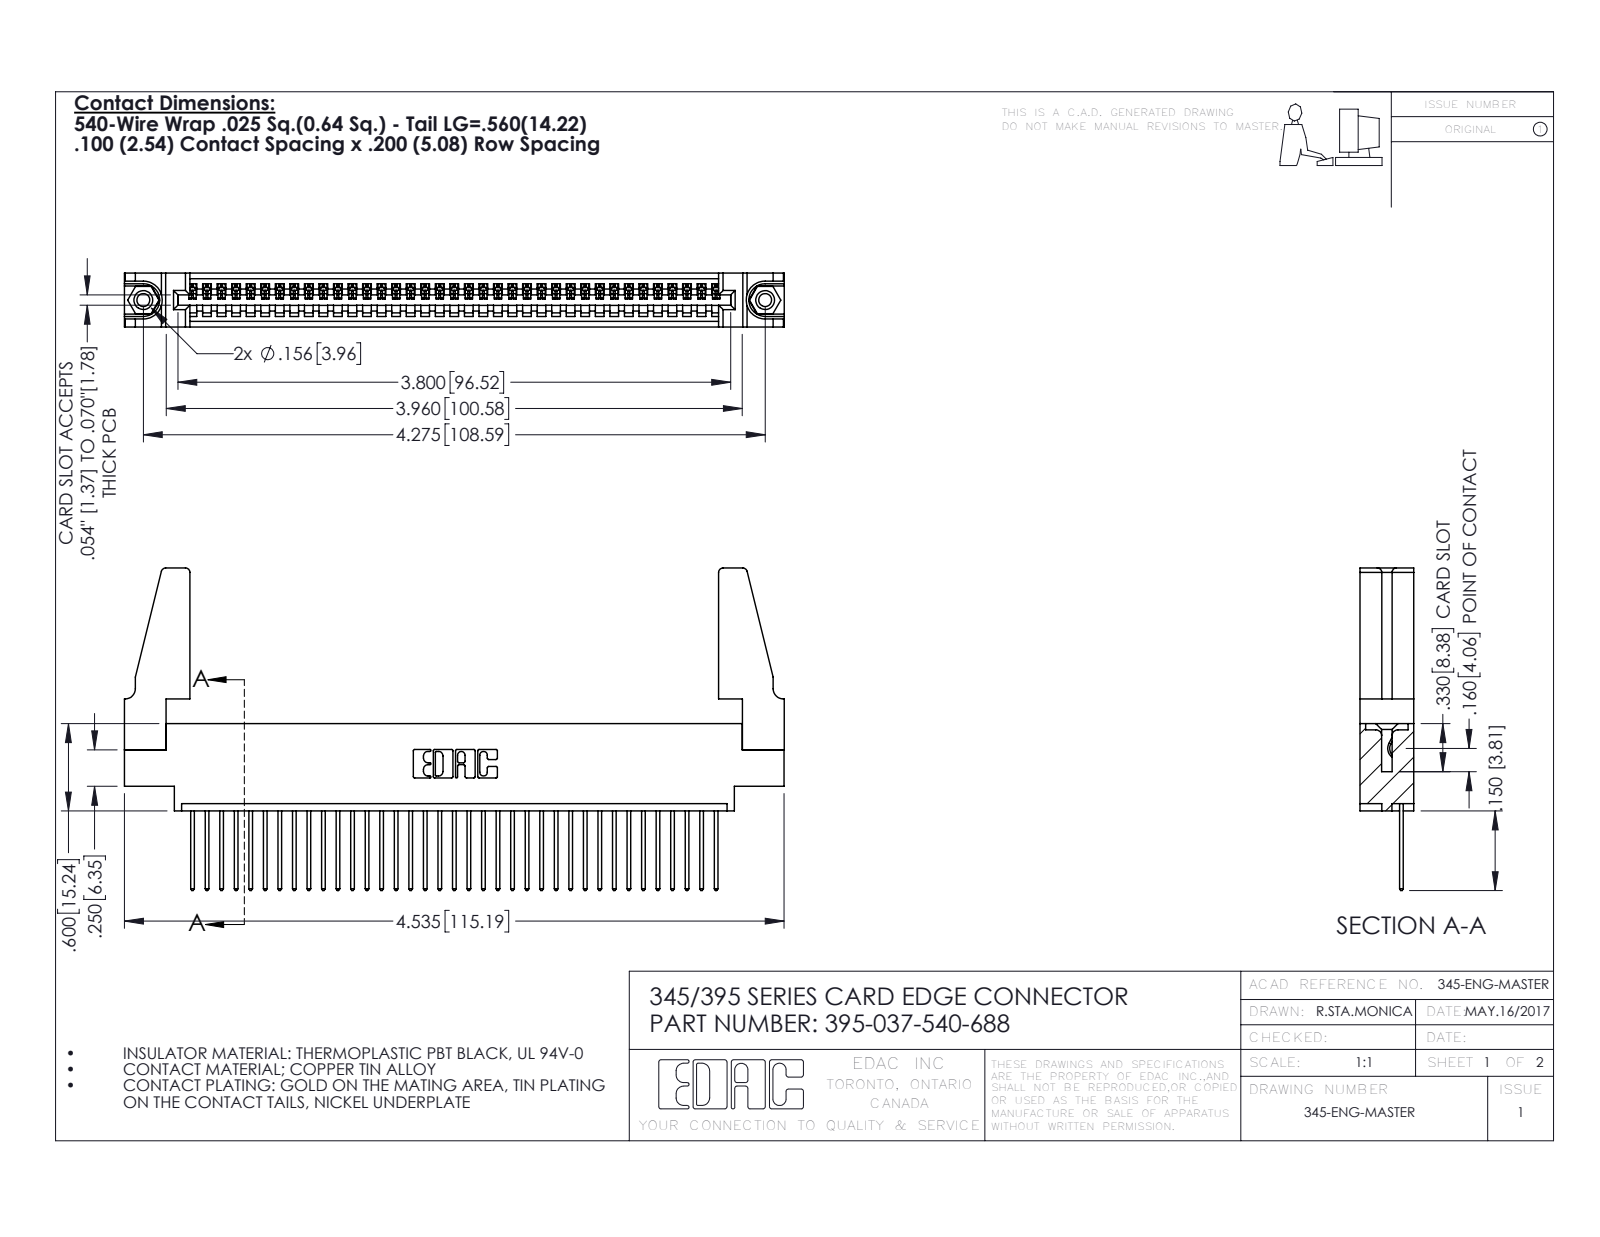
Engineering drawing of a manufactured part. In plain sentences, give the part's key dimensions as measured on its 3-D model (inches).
The part is named "345-220-078_345-220-088; 345-250-001_345-250-001-102; 345 Part_0.170 Offset - 0.156 Dia-TH; 345-292-001_345-293-140 (+1 more)". Its 3-D file was written by "SolidWorks 2016 (CONFIG_CONTROL_DESIGN)". It is 42 solids with 2400 faces: 1636 planar, 748 cylindrical and 16 other. Overall it measures 4.536 by 2.217 by 0.37 inches. Its volume is 0.86 cubic inches and its surface area 27.83 square inches. Round holes: 2 of diameter 0.089, 2 of diameter 0.125, 2 of diameter 0.156, 1 of diameter 0.064. Round bosses or shafts: 2 of diameter 0.155. Partial cylindrical surfaces (rounded edges, fillets, slot ends): 74 of radius 0.006, 74 of radius 0.01, 22 of radius 0.01, 8 of radius 0.03, 6 of radius 0.007, 6 of radius 0.031, 3 of radius 0.026, 2 of radius 0.031. The main face-to-face distances are 0.072, 0.298, 0.37, 0.098, 0.272, 0.025, 0.2, 0.225, 0.175, 0.149. The hole center spacings are 0.27, 4.039, 4.275.
